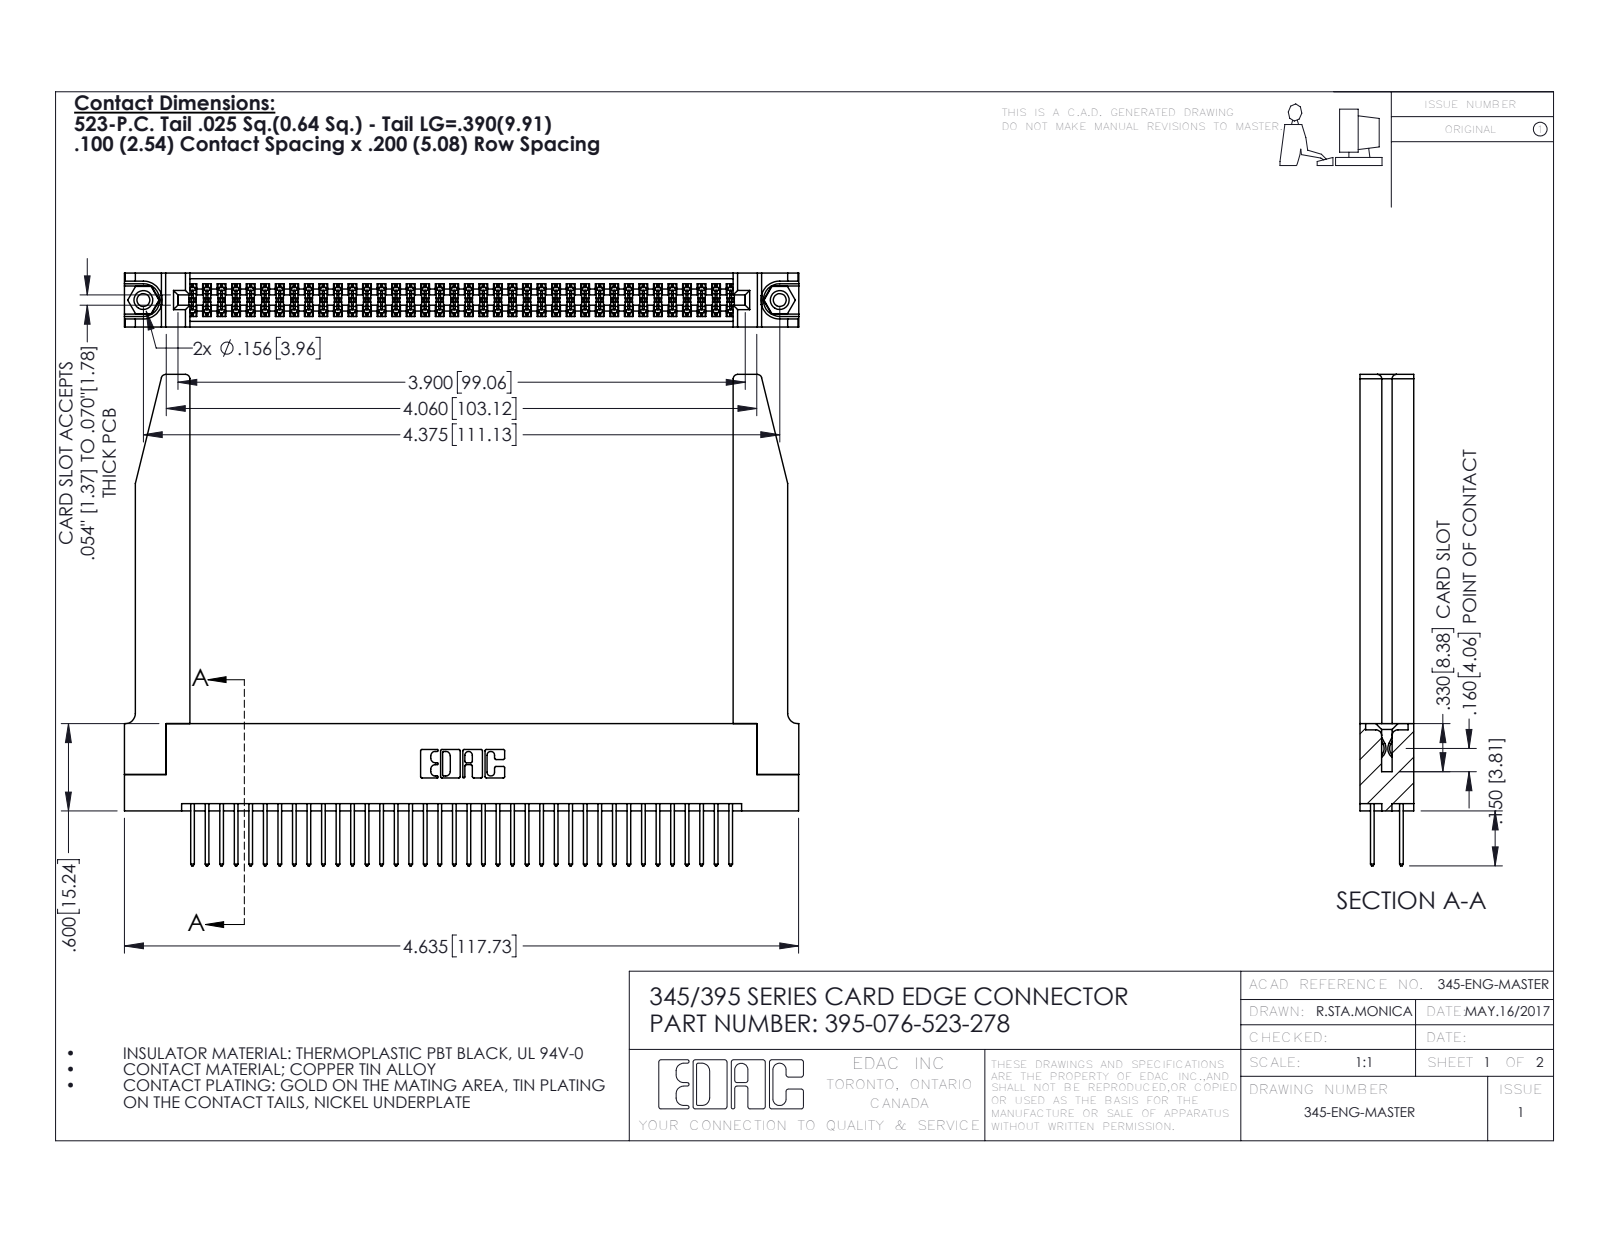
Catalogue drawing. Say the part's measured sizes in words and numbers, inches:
The part is named "345 Part_Flush Mounting Lugs - 0.156 Dia-TH; 345-292-001_345-293-123; 345-250-001_345-250-001-102; 345-220-078_345-220-078 (+1 more)". Its 3-D file was written by "SolidWorks 2016 (CONFIG_CONTROL_DESIGN)". It is 81 solids with 4160 faces: 2730 planar, 1378 cylindrical and 52 other. Overall it measures 4.636 by 3.377 by 0.37 inches. Its volume is 1.179 cubic inches and its surface area 38.04 square inches. Round holes: 2 of diameter 0.089, 2 of diameter 0.125, 2 of diameter 0.156, 1 of diameter 0.064. Round bosses or shafts: 2 of diameter 0.155. Partial cylindrical surfaces (rounded edges, fillets, slot ends): 114 of radius 0.006, 76 of radius 0.01, 22 of radius 0.01, 8 of radius 0.03, 6 of radius 0.007, 6 of radius 0.031, 3 of radius 0.026, 2 of radius 0.014. The main face-to-face distances are 0.072, 0.298, 0.37, 0.2, 0.098, 0.272, 0.025, 0.225, 0.175, 0.148. The hole center spacings are 0.27, 4.139, 4.375.
